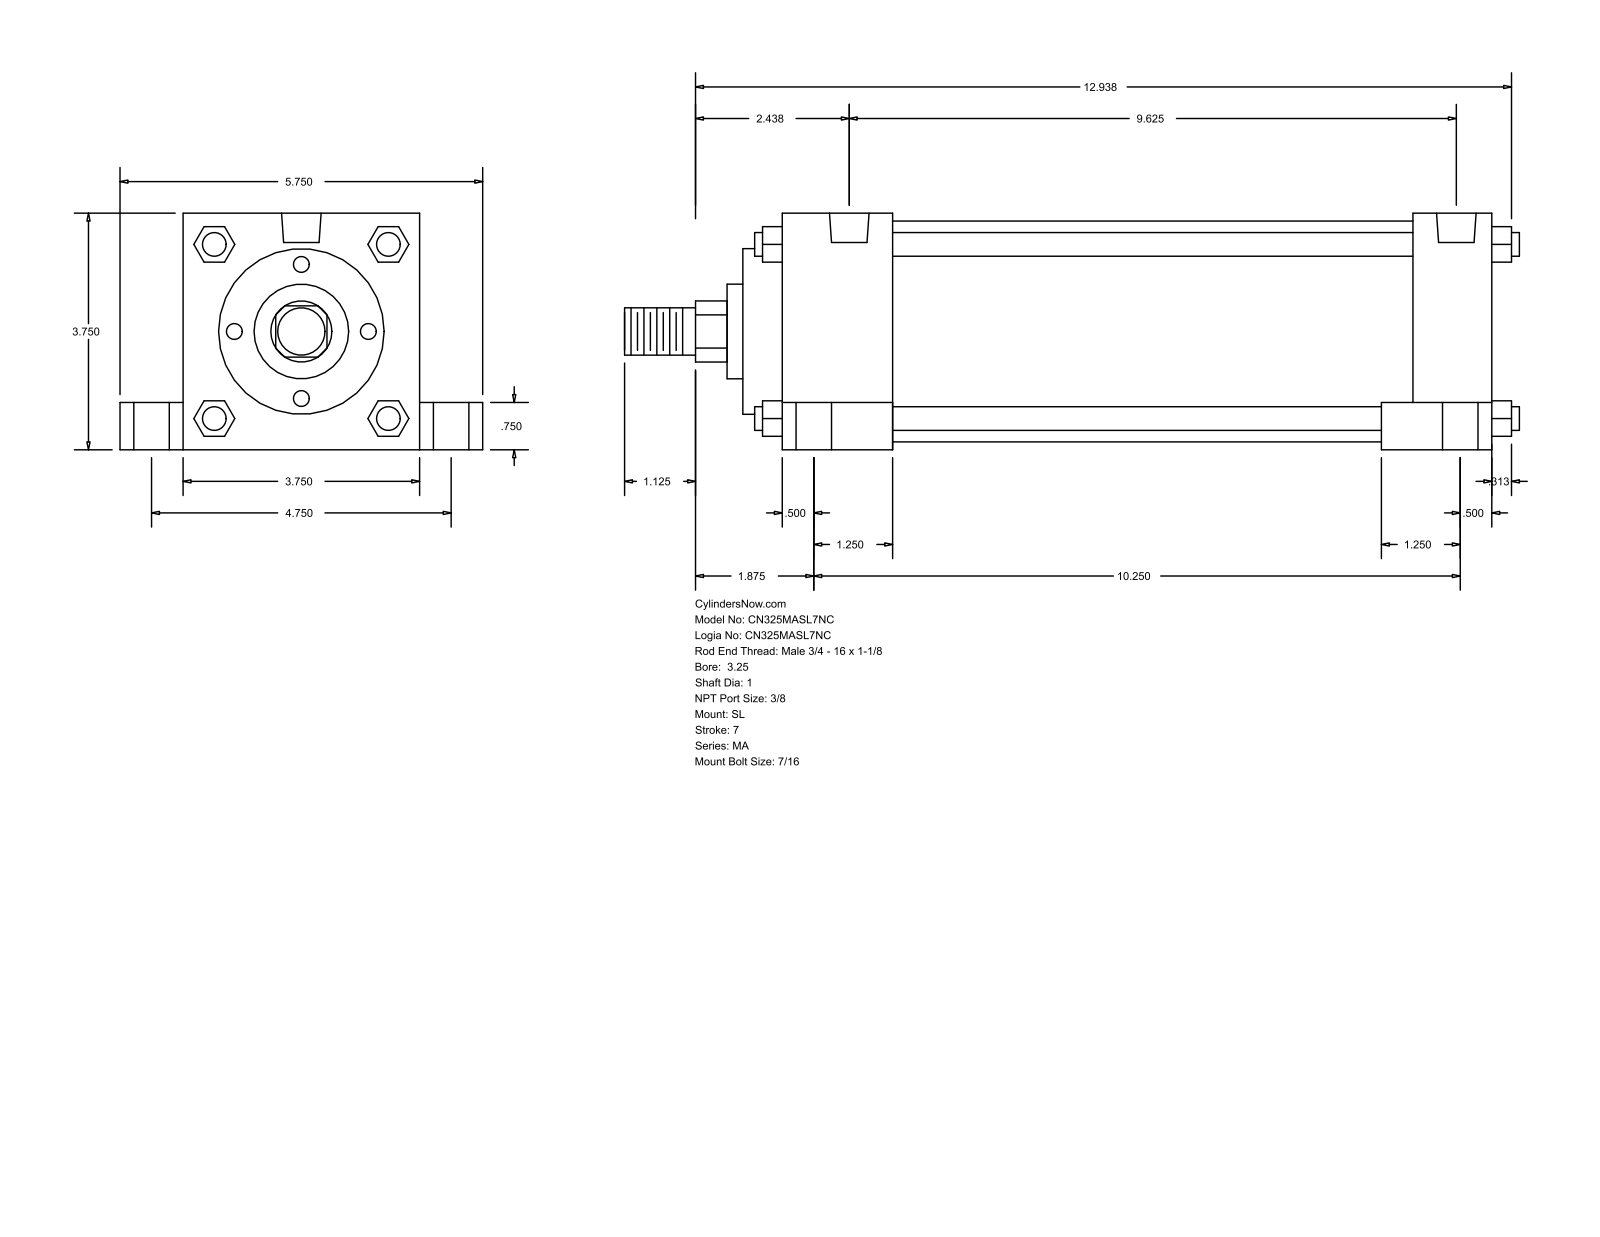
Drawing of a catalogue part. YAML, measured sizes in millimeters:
part_name: "MA_SL__0325_1"
step_written_by: "GSSL Pune (CONFIG_CONTROL_DESIGN)"
units: millimeters
bodies: {solids: 0, faces: 150, planar: 113, cylindrical: 37, other: 0}
overall_size: [360.36, 146.05, 95.25]
round_holes:
  - {diameter: 11.11, count: 4}
  - {diameter: 14.29, count: 4}
  - {diameter: 20.64, count: 4}
  - {diameter: 15.93, count: 2}
round_bosses_or_shafts:
  - {diameter: 9.53, count: 4}
  - {diameter: 88.9, count: 1}
  - {diameter: 66.67, count: 1}
  - {diameter: 38.1, count: 1}
  - {diameter: 25.4, count: 1}
  - {diameter: 19.05, count: 1}
partial_cylinders:
  - {radius: 12.29, count: 1}
face_to_face_distances: [95.24, 285.76, 209.55, 15.87, 25.41, 120.65, 19.05, 254.01, 31.75, 44.46]
hole_center_spacings: [60.35, 60.66, 62, 63.27, 120.66, 234.95, 248.74, 253.36]
